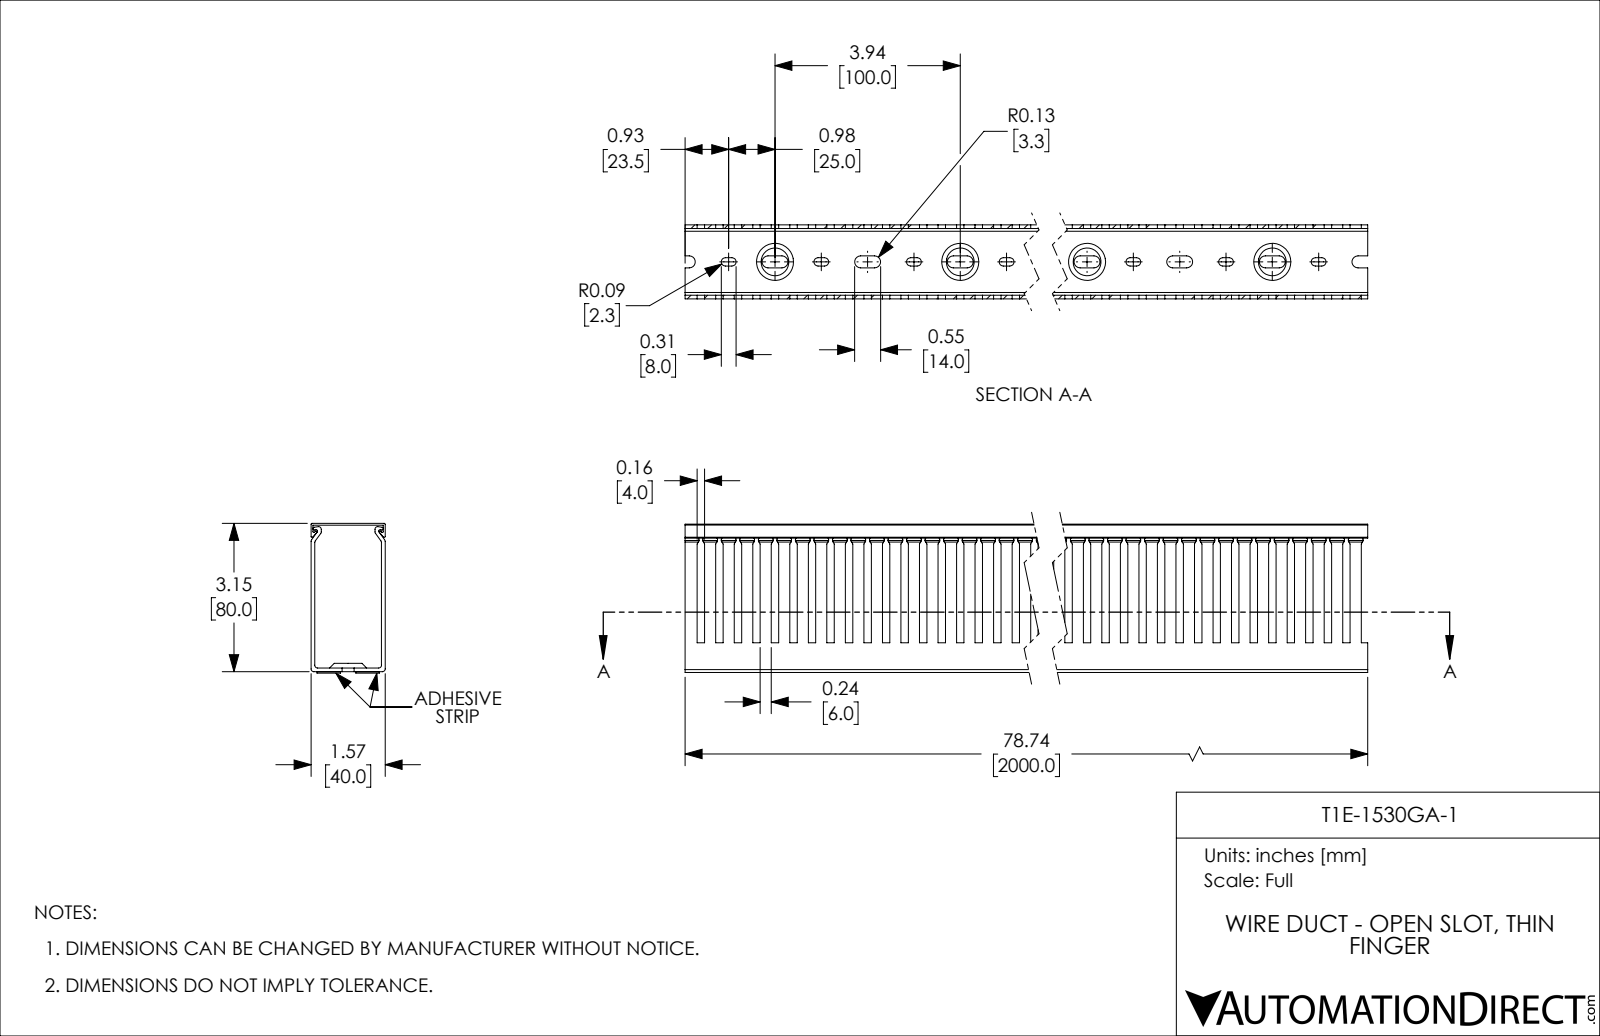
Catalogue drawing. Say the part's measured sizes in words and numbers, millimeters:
The part is named "T1E-1530GA-1". Its 3-D file was written by "SolidWorks 2021 (CONFIG_CONTROL_DESIGN)". It is 4 solids with 1017 faces: 546 planar, 431 cylindrical and 40 other. Overall it measures 2000 by 80.79 by 40 millimeters. Its volume is 939 863 cubic millimeters and its surface area 1 125 000 square millimeters. Partial cylindrical surfaces (rounded edges, fillets, slot ends): 80 of radius 2.25, 80 of radius 3.25, 12 of radius 1.5, 8 of radius 0.5, 6 of radius 0.75. The main face-to-face distances are 2, 38, 40, 36, 1, 80, 79, 77, 78, 0.79.
